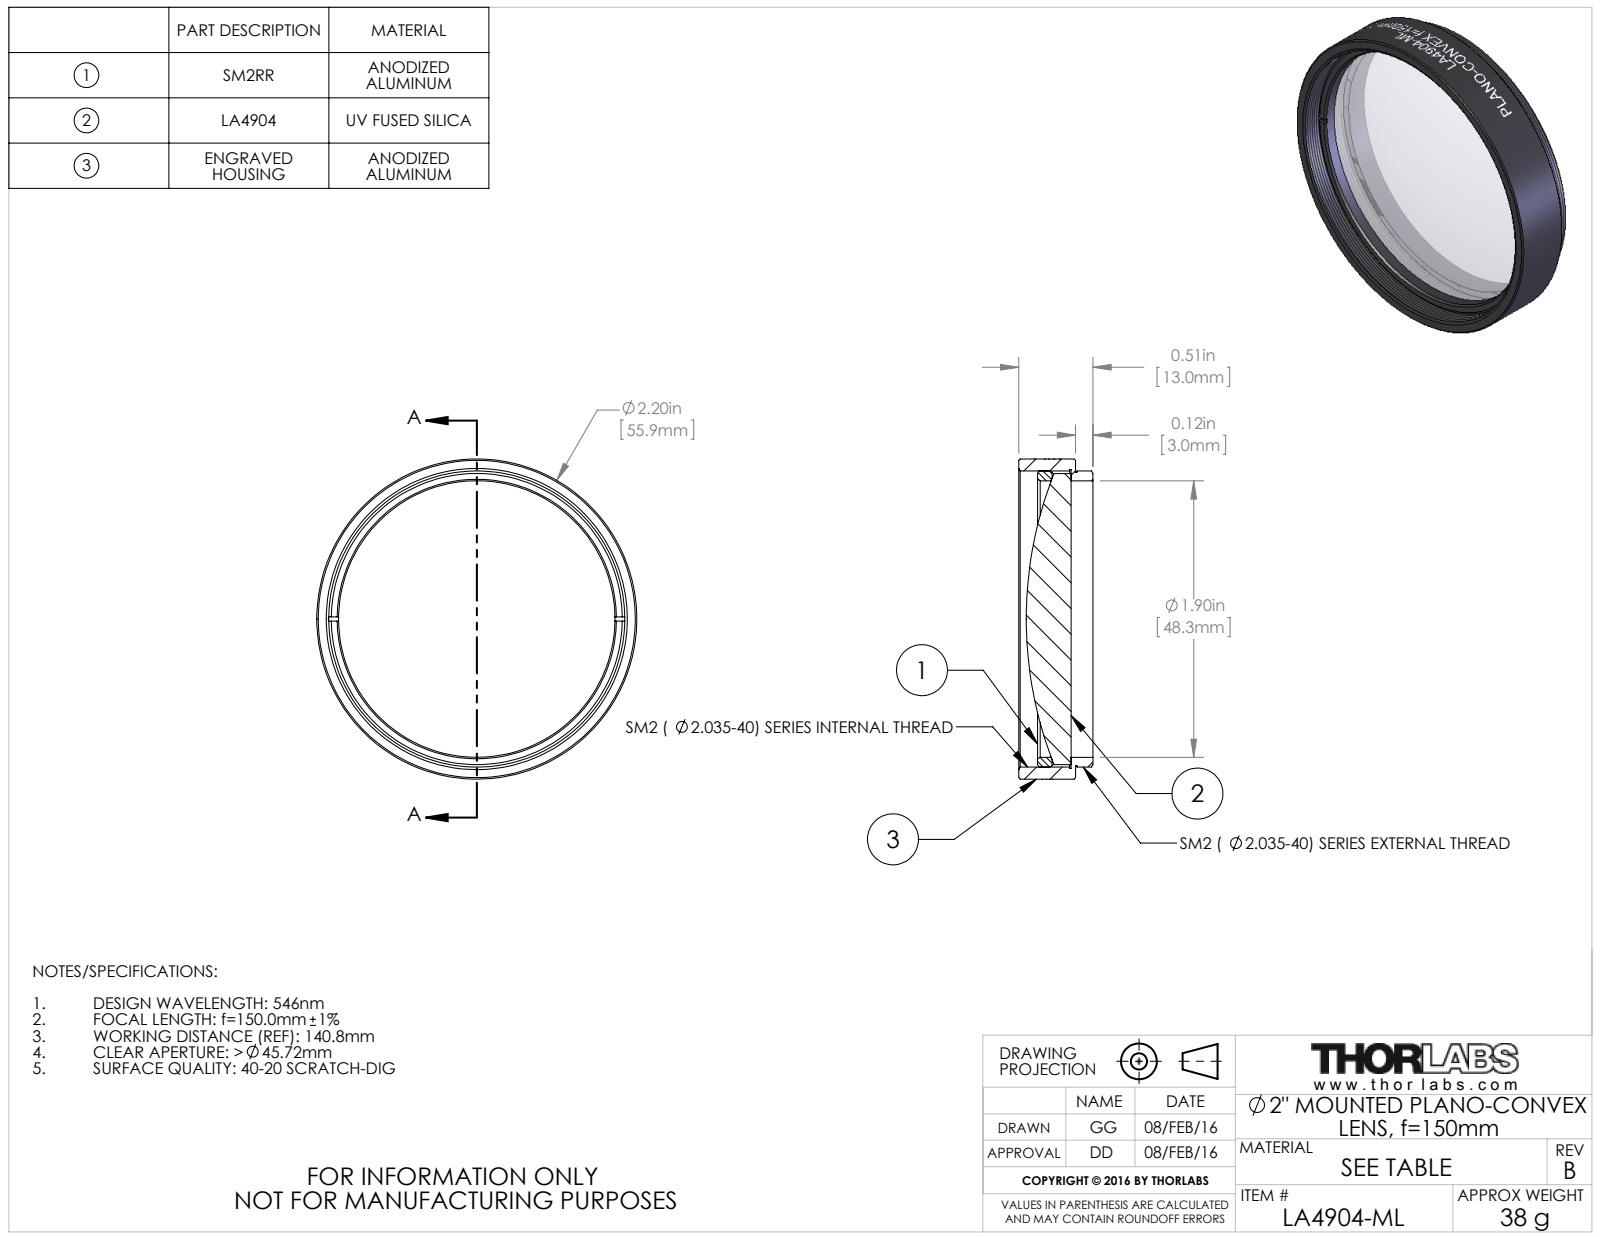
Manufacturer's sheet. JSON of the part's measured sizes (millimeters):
{"part_name": "TTN039430-E0W", "step_written_by": "SolidWorks 2014 (CONFIG_CONTROL_DESIGN)", "units": "millimeters", "bodies": {"solids": 3, "faces": 110, "planar": 16, "cylindrical": 74, "other": 20}, "overall_size": [55.88, 55.88, 12.95], "volume_mm3": 16177, "surface_area_mm2": 11423, "round_holes": [[48.26, 1], [52.2, 1]], "round_bosses_or_shafts": [[55.88, 1], [51.69, 1], [51.18, 1], [50.8, 1]], "face_to_face_distances": [0.76, 9.91, 9.15, 3.05, 3.81, 12.96, 7.14, 4.09, 3.33, 5.82]}
